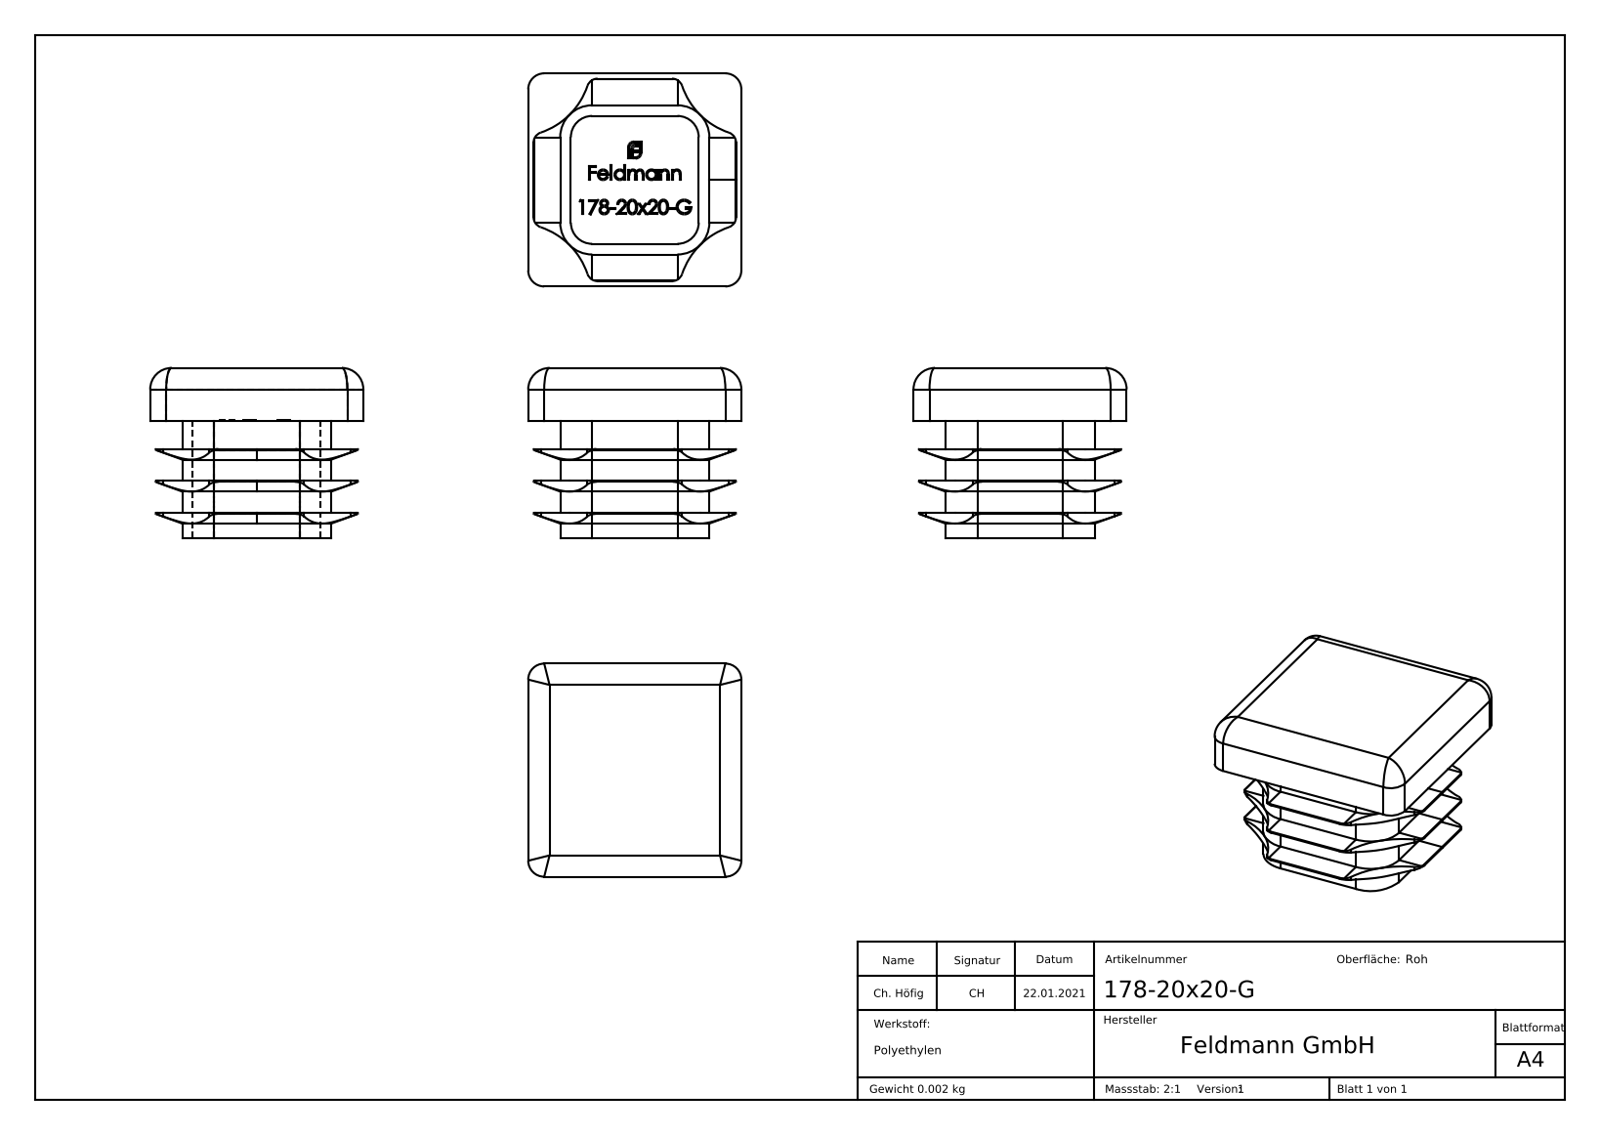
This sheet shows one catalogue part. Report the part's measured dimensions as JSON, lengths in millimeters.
{"part_name": "178-20x20-G", "step_written_by": "SolidWorks 2018 (CONFIG_CONTROL_DESIGN)", "units": "millimeters", "bodies": {"solids": 1, "faces": 462, "planar": 231, "cylindrical": 79, "other": 152}, "overall_size": [20, 20, 16], "volume_mm3": 2613, "surface_area_mm2": 2681, "partial_cylinders_radius": [[1, 8], [2, 8], [1.5, 4], [3, 4], [7, 4]], "face_to_face_distances": [3, 5, 1, 13, 16, 4, 17, 12, 14, 20]}
